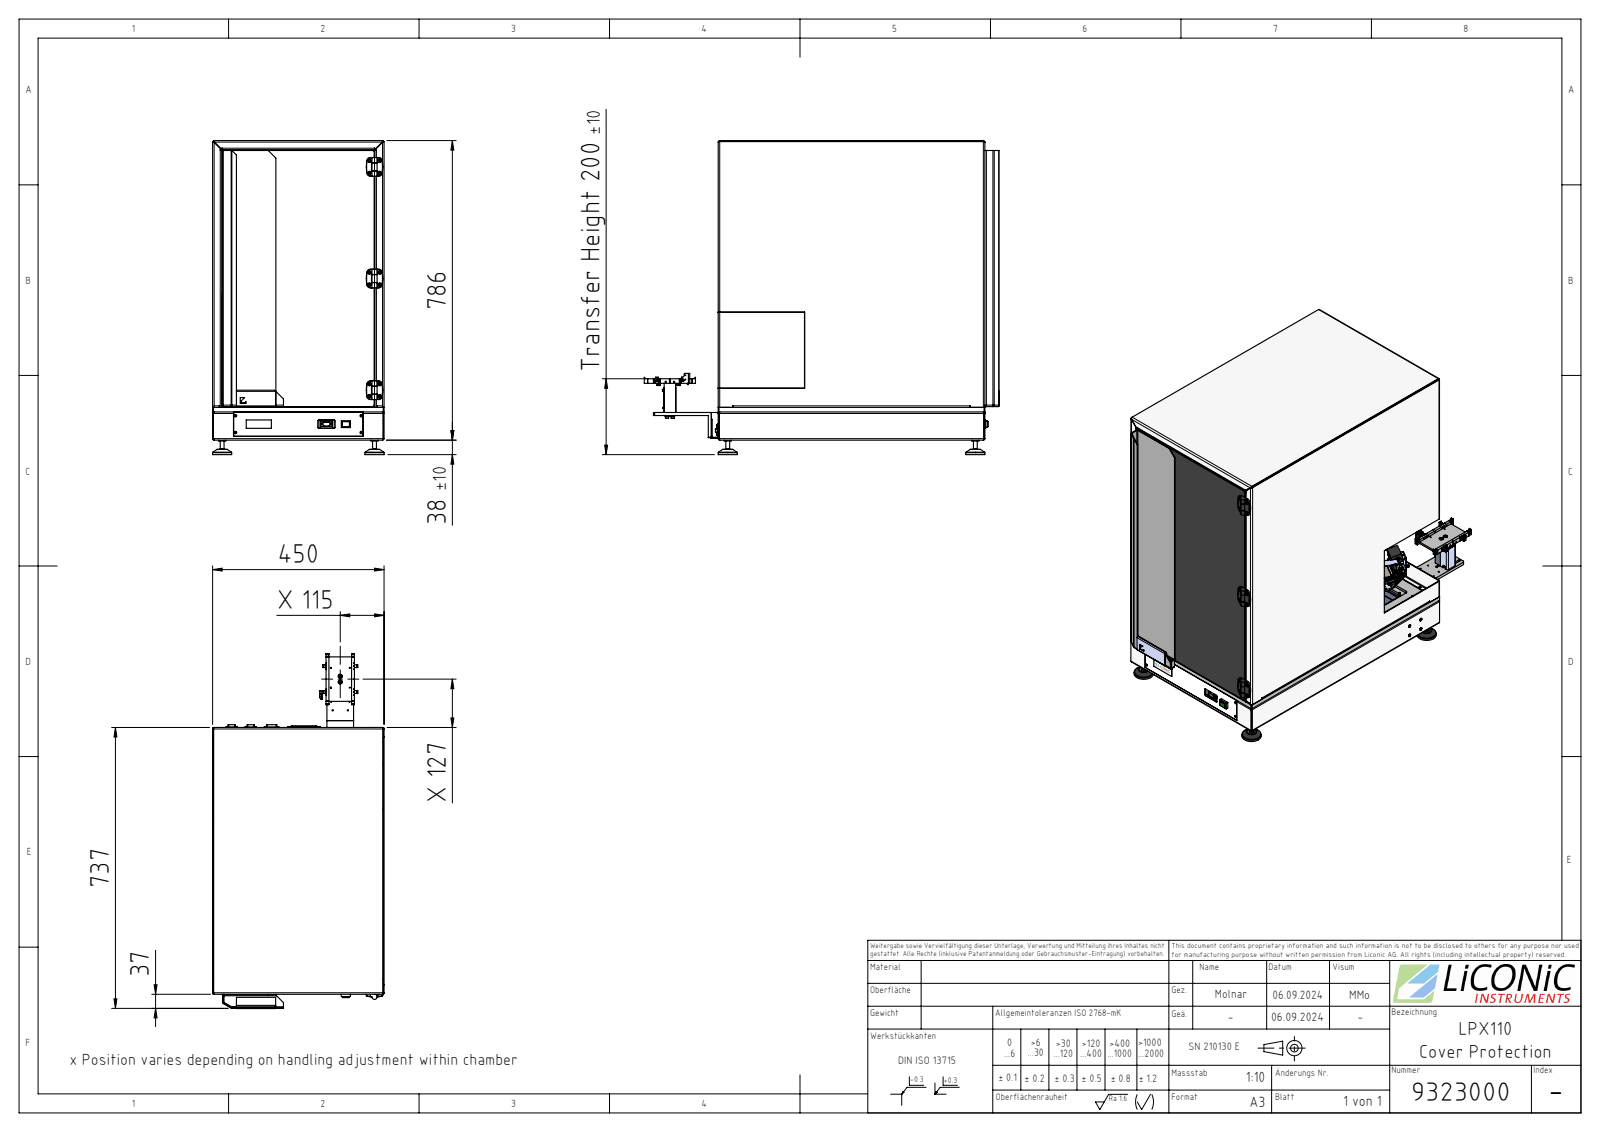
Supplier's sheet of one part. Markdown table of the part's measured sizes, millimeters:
| quantity | value |
| --- | --- |
| part name | 9323000 |
| STEP written by | SolidWorks 2022 (AUTOMOTIVE_DESIGN) |
| units | millimeters |
| bodies | 46 solids, 6145 faces (3452 planar, 2536 cylindrical, 157 other) |
| overall size | 931.54 × 824 × 450.01 |
| volume | 11 760 000 mm³ |
| surface area | 6 759 000 mm² |
| round holes (diameter × count) | 2.5 × 51, 4 × 50, 3.3 × 25, 4.2 × 23, 6.5 × 21, 6 × 16, 4.5 × 14, 3 × 12, 9 × 12, 3.4 × 10, 3.1 × 8, 7.1 × 8 |
| round bosses / shafts (diameter × count) | 4 × 6, 50.01 × 4, 10 × 4, 1.5 × 3, 392 × 1, 86 × 1, 15.5 × 1, 14.5 × 1 |
| partial cylindrical surfaces (radius × count) | 0.1 × 572, 0.25 × 572, 2 × 289, 2.5 × 110, 1 × 72, 5 × 65, 4 × 40, 3 × 20 |
| main face-to-face distances | 2, 448, 700, 698, 784, 450, 446, 712, 72, 12 |
| hole center spacings | 23, 46, 69, 92, 115, 138, 161, 184 |
